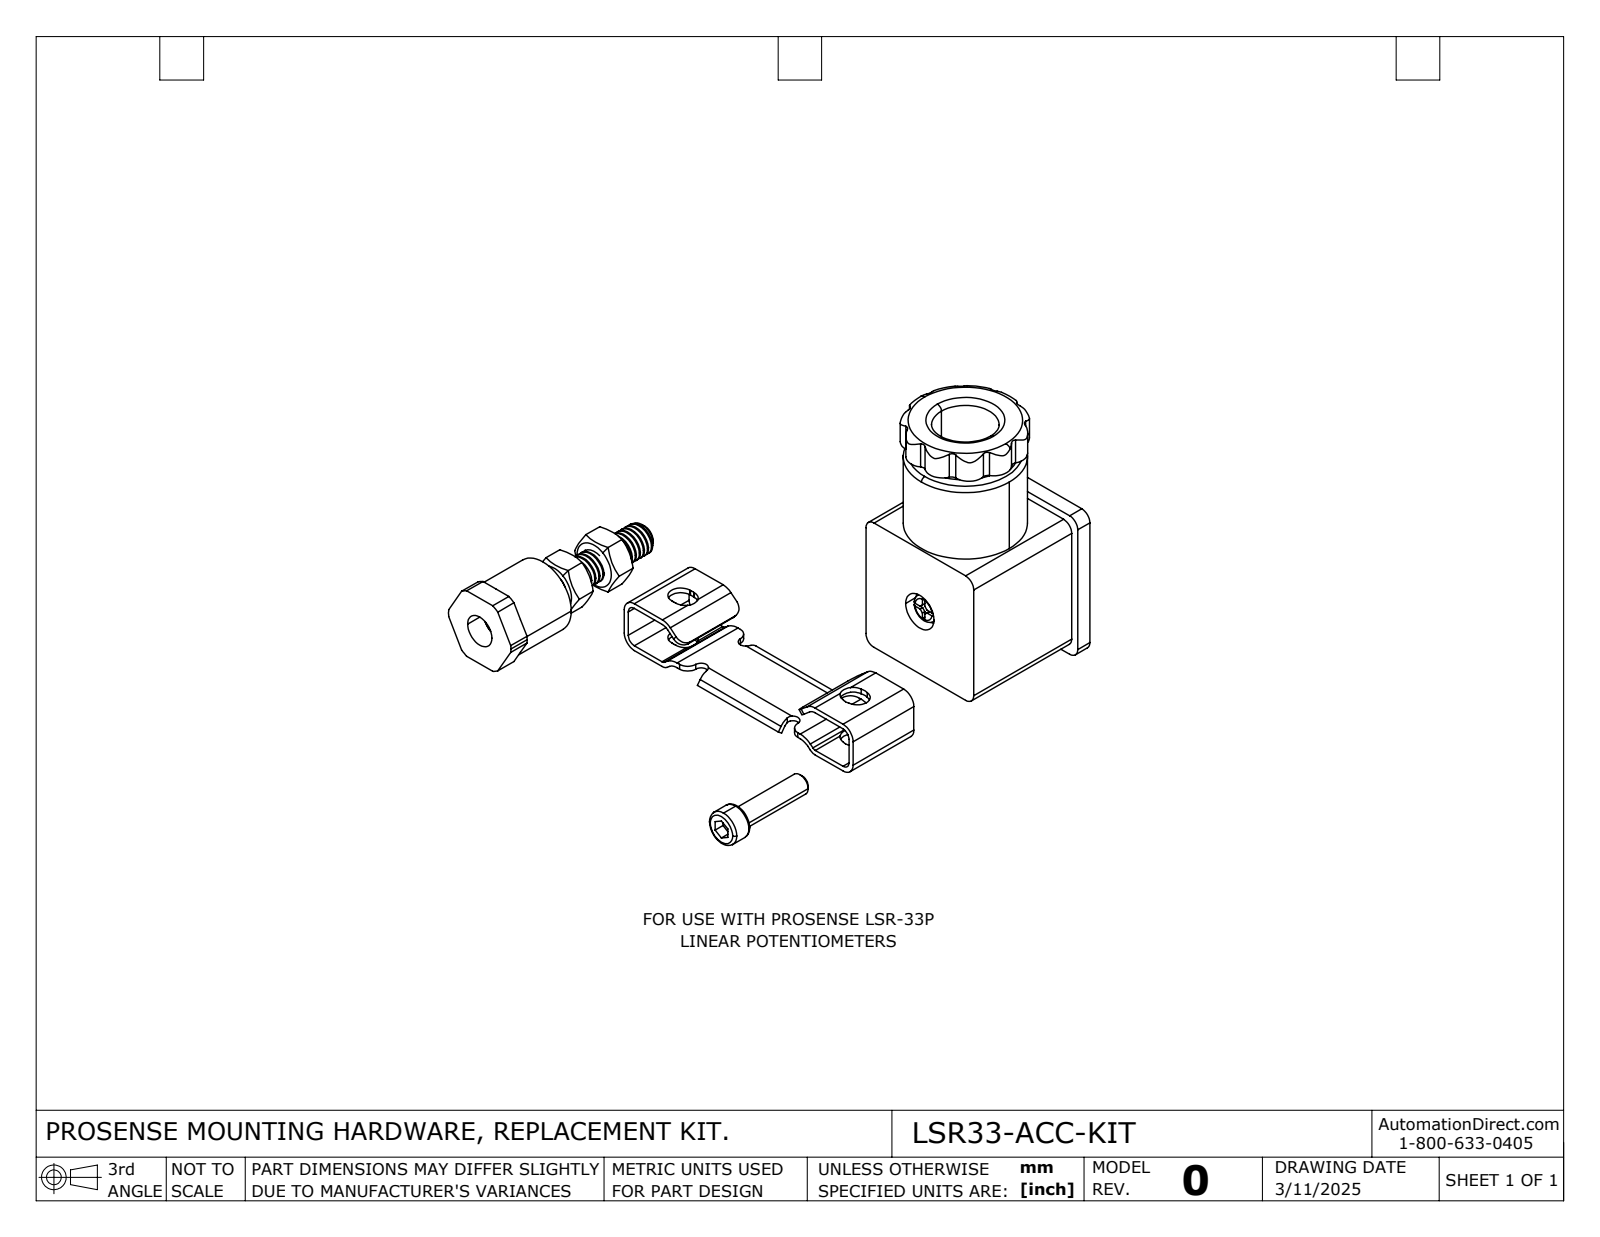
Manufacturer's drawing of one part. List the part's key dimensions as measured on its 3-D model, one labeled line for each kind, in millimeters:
Part name (STEP PRODUCT): LSR33-ACC-KIT
STEP written by: SolidWorks 2024 (AUTOMOTIVE_DESIGN)
Units: millimetres
Bodies: 10 solids, 555 faces (213 planar, 297 cylindrical, 45 other)
Overall size (bounding box): 97.88 × 65.1 × 50.1
Volume: 21 673 mm³ · Surface area: 22 251 mm²
Round holes (diameter × count): ⌀2.8 ×1, ⌀5.2 ×1, ⌀5.3 ×1, ⌀5.9 ×1, ⌀7 ×1, ⌀10 ×1, ⌀11.8 ×1, ⌀15.3 ×1, ⌀22 ×1
Round bosses / shafts (diameter × count): ⌀21.7 ×1, ⌀17 ×1, ⌀14 ×1, ⌀12.8 ×1, ⌀6.5 ×1, ⌀6.3 ×1, ⌀6.19 ×1, ⌀6 ×1
Partial cylindrical surfaces — rounded edges, fillets, slot ends (radius × count): R2 ×20, R1 ×13, R3.1 ×11, R0.5 ×8, R1.5 ×6, R3 ×6, R1.3 ×4, R2.25 ×4
Main face-to-face distances: 1.6, 25, 23.4, 1, 1.8, 24, 26.6, 23.2, 24.8, 2
Hole centre spacings: 43.27, 43.35
